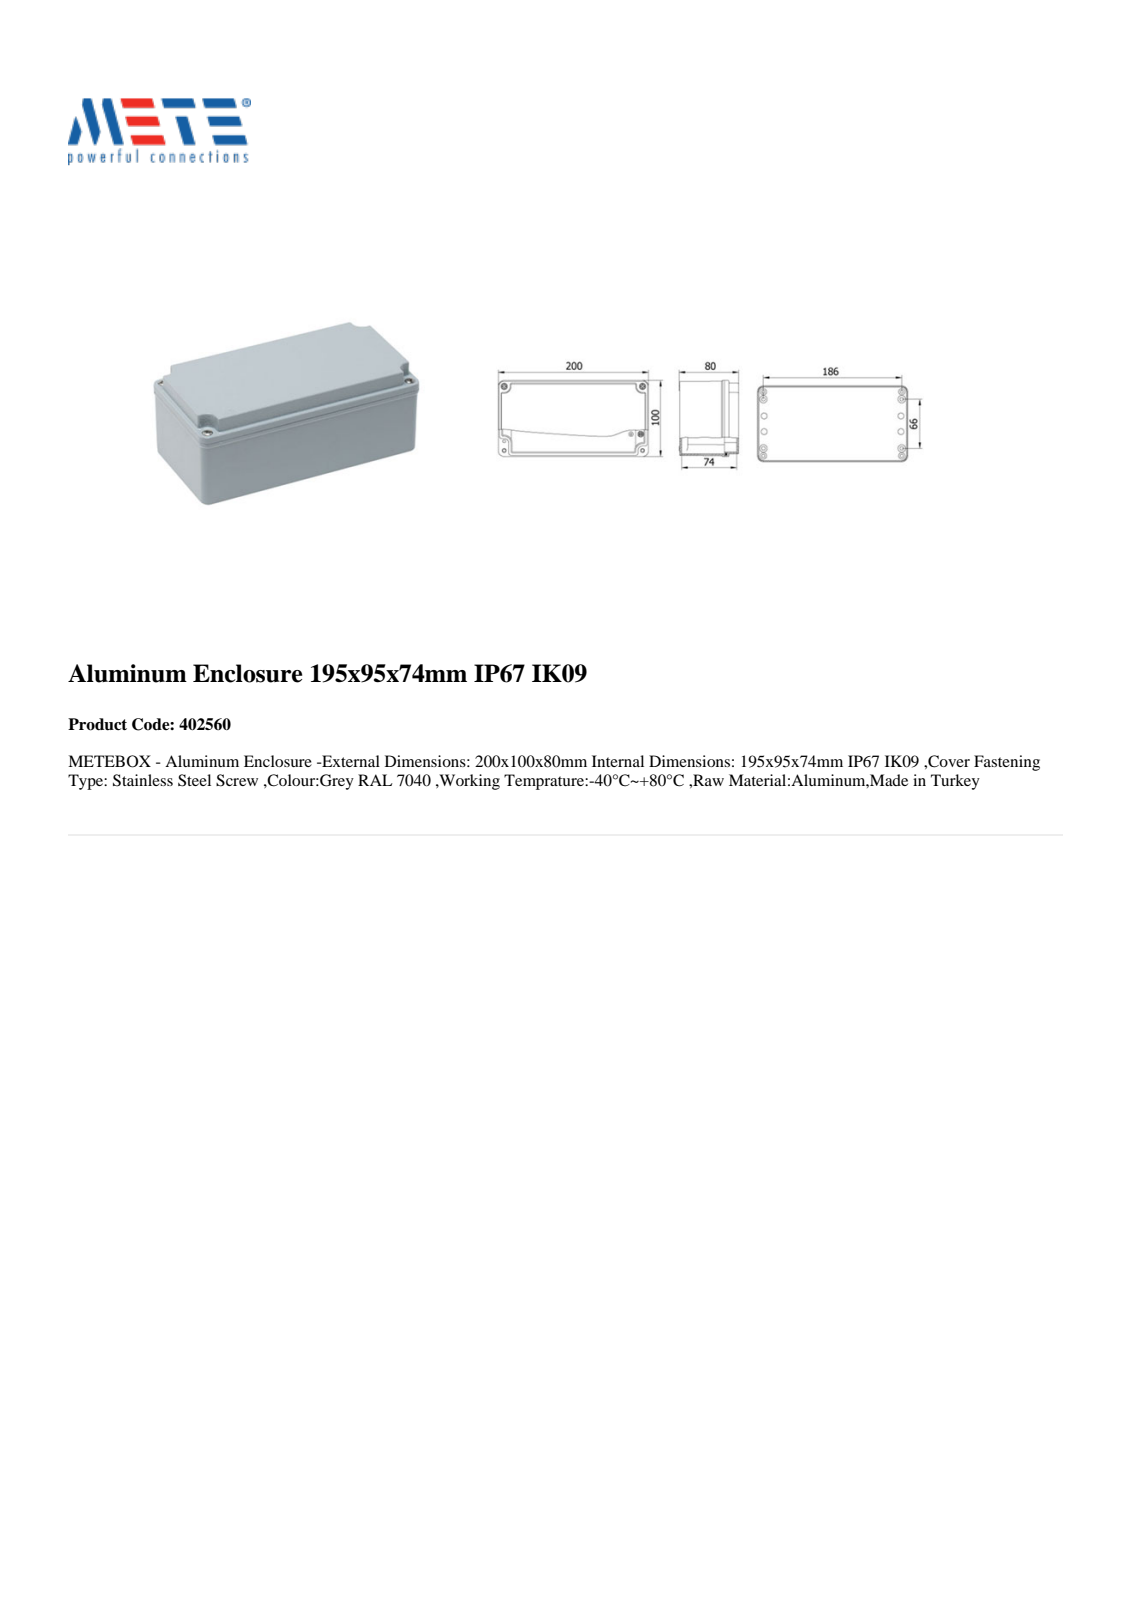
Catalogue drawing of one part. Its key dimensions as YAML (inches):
part_name: "mtas123C19991ban"
step_written_by: "SIEMENS PLM Software NX 8.0 (AP203_CONFIGURATION_CONTROLLED_3D_DESIGN_OF_MECHANICAL_PARTS_AND_ASSEMBLIES_MIM_LF)"
units: inches
bodies: {solids: 7, faces: 905, planar: 244, cylindrical: 223, other: 438}
overall_size: [9.552, 5.591, 4.016]
volume: 18.07
surface_area: 262.2
round_holes:
  - {diameter: 0.138, count: 1}
round_bosses_or_shafts:
  - {diameter: 0.394, count: 4}
  - {diameter: 0.157, count: 4}
  - {diameter: 0.315, count: 1}
  - {diameter: 0.151, count: 1}
  - {diameter: 0.118, count: 1}
partial_cylinders:
  - {radius: 0.004, count: 79}
  - {radius: 0.039, count: 44}
  - {radius: 0.008, count: 40}
  - {radius: 0.02, count: 8}
  - {radius: 0.079, count: 4}
face_to_face_distances: [0.098, 3.012, 0.099, 3.11, 2.913, 2.362, 0.65, 2.264, 0.748, 3.626]
